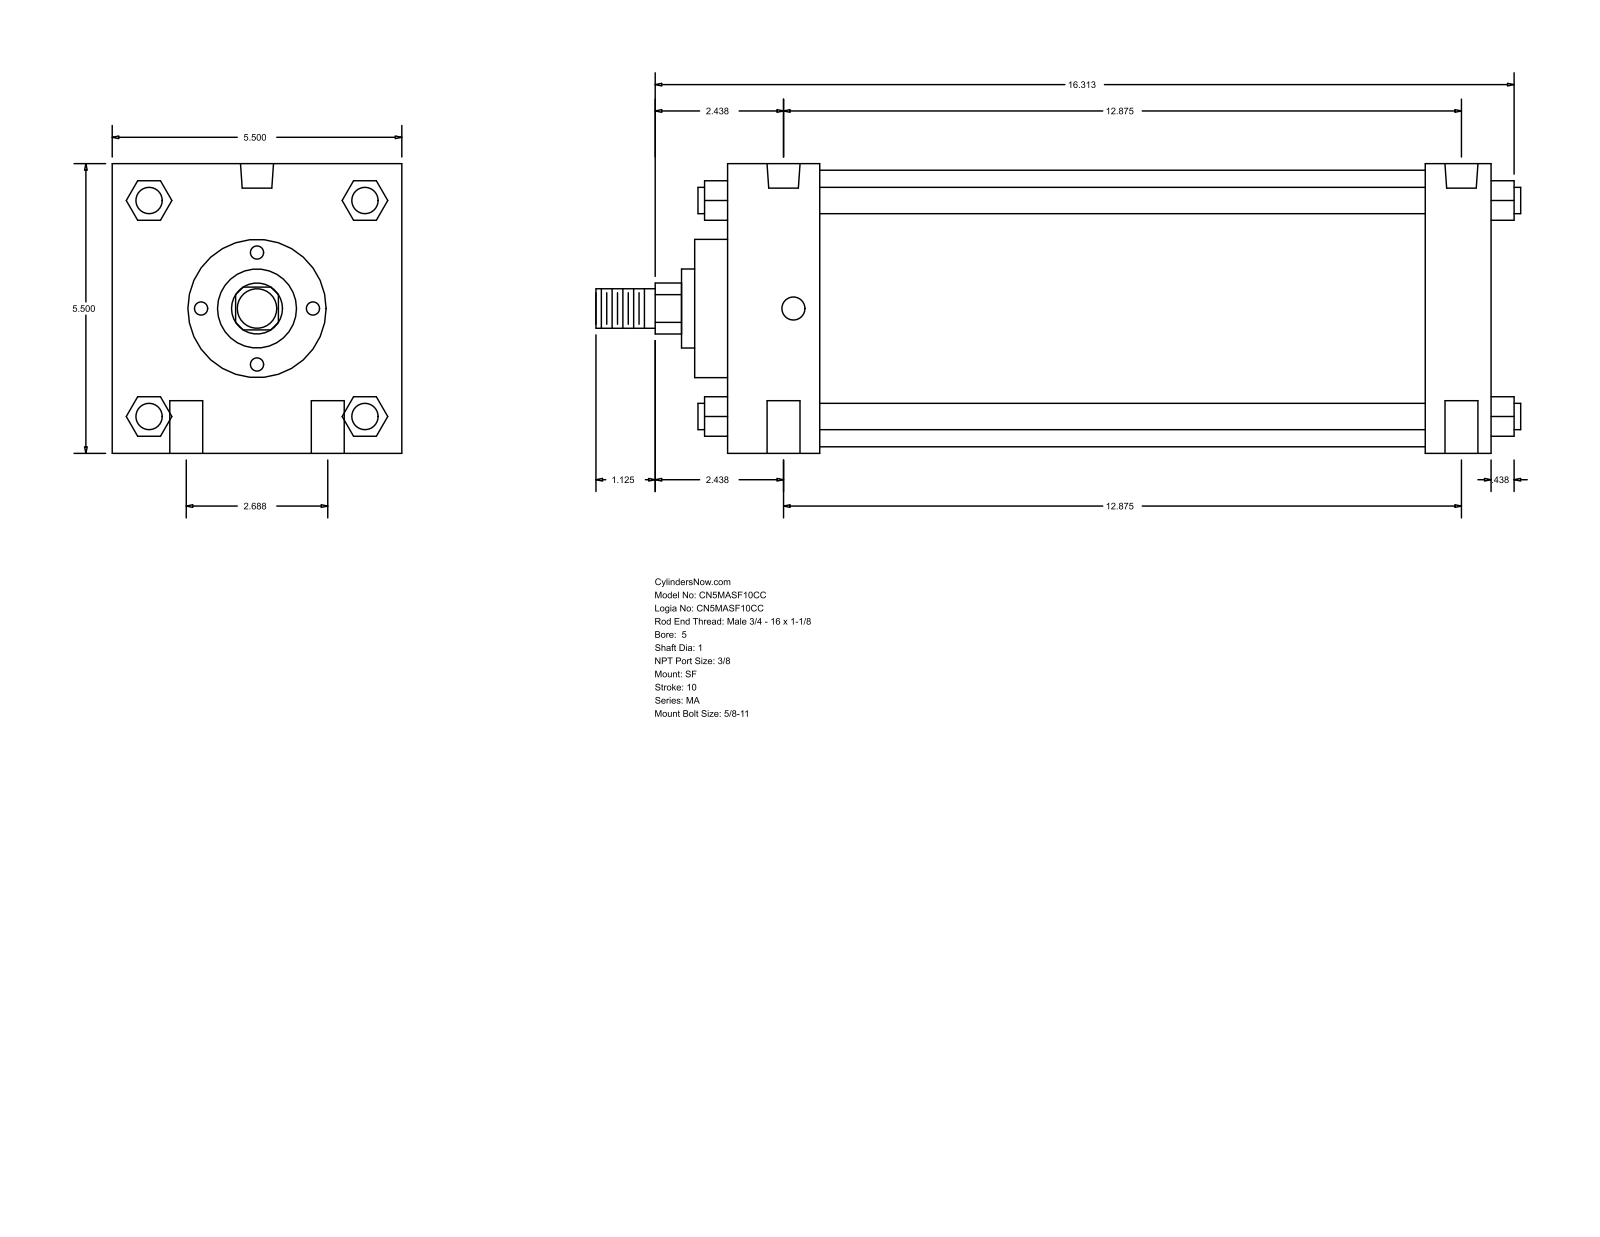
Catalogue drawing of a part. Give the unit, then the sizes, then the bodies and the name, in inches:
Units: inches
Overall size (bounding box): 17.563 × 5.5 × 5.5
Round holes (diameter × count): ⌀0.625 ×4, ⌀0.437 ×2, ⌀0.627 ×2
Round bosses / shafts (diameter × count): ⌀0.5 ×4, ⌀5.25 ×1, ⌀2.625 ×1, ⌀1.5 ×1, ⌀1 ×1, ⌀0.75 ×1
Partial cylindrical surfaces — rounded edges, fillets, slot ends (radius × count): R0.484 ×1
Main face-to-face distances: 5.5, 14.5, 1.75, 13.25, 11.5, 12.75, 1.25, 0.625, 2.375, 13.875
Hole centre spacings: 1.344, 12.945, 12.875, 2.687, 13.153, 12.5
Bodies: 0 solids, 126 faces (95 planar, 31 cylindrical, 0 other)
Part name (STEP PRODUCT): MA_SF__0500_1
STEP written by: GSSL Pune (CONFIG_CONTROL_DESIGN)
